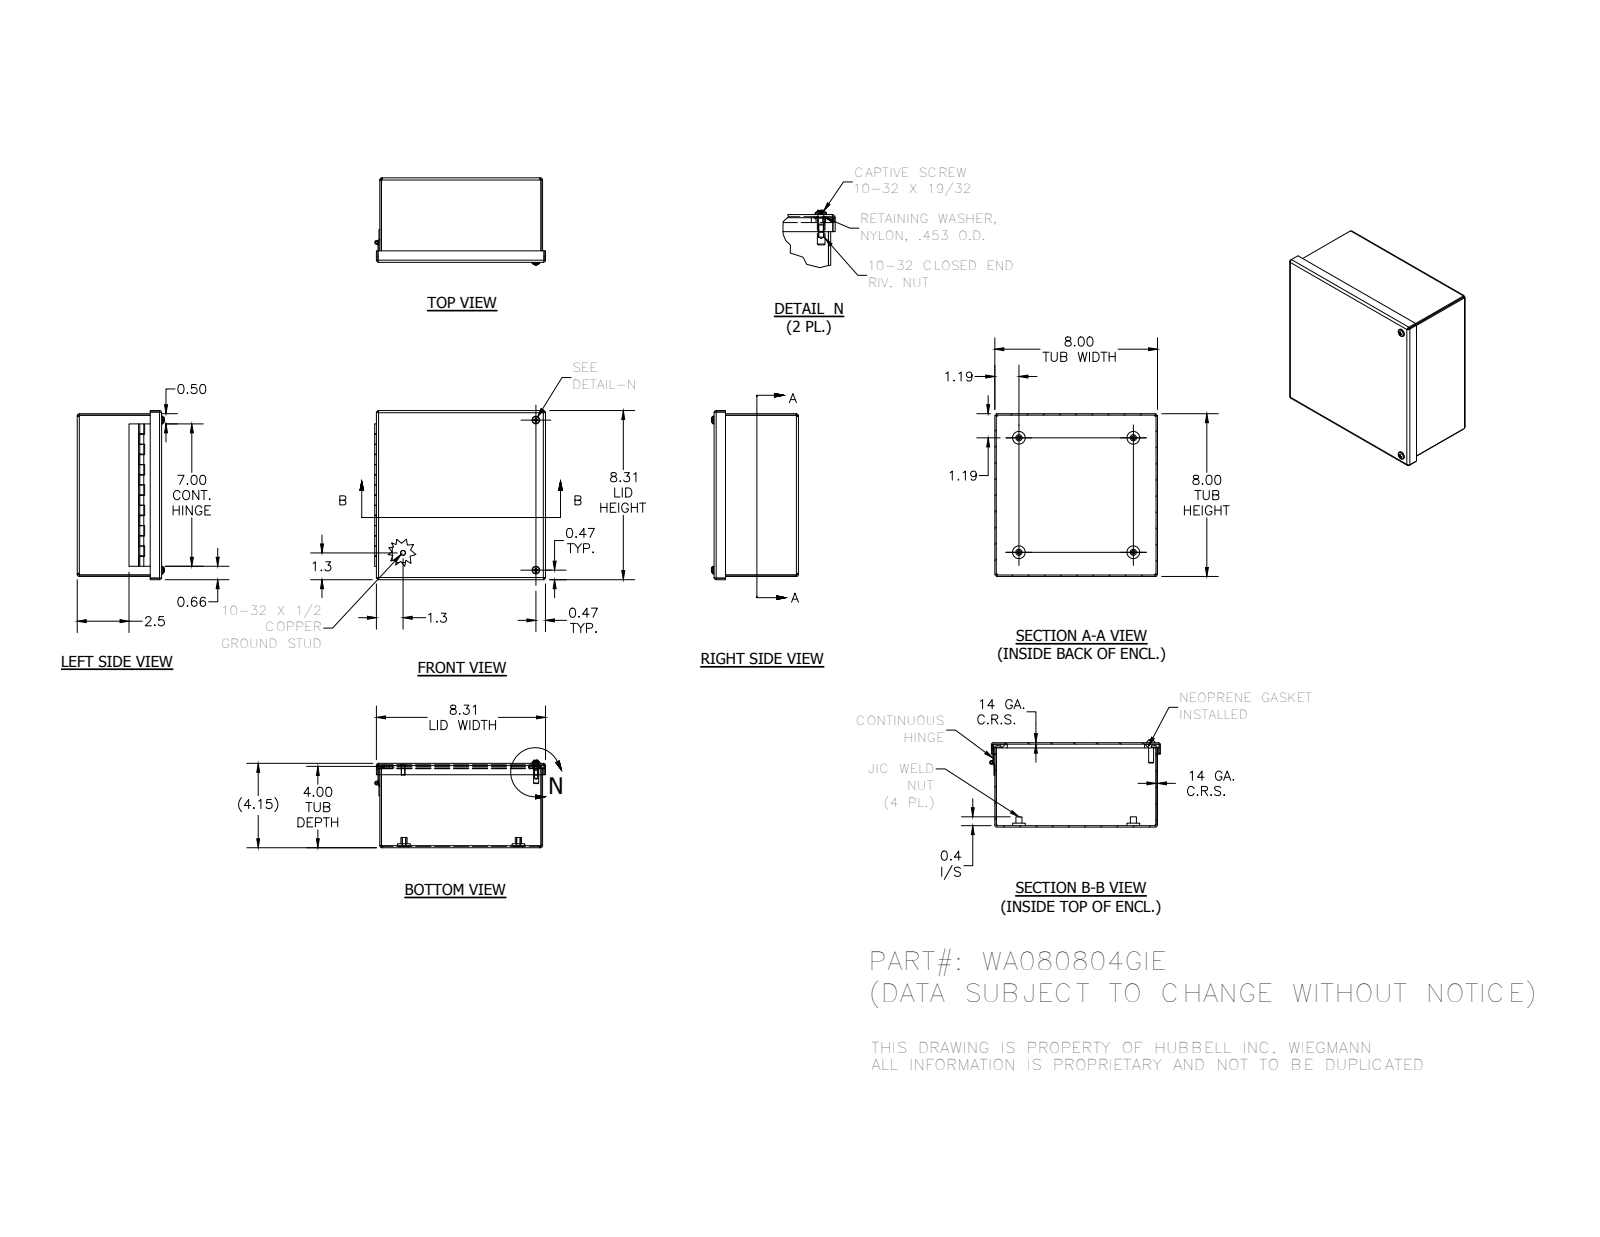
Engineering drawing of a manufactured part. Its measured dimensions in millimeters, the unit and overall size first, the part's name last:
Units: millimetres
Overall size (bounding box): 213.28 × 211.14 × 108.77
Round holes (diameter × count): ⌀3.96 ×6, ⌀6.53 ×4, ⌀7.94 ×4, ⌀4.98 ×2, ⌀7.06 ×2, ⌀7.14 ×2, ⌀2.96 ×1
Round bosses / shafts (diameter × count): ⌀15.88 ×4, ⌀7.62 ×4, ⌀4.83 ×3, ⌀11.51 ×2, ⌀10.31 ×2, ⌀9.47 ×2, ⌀6.3 ×2, ⌀6.35 ×1
Partial cylindrical surfaces — rounded edges, fillets, slot ends (radius × count): R0.79 ×12, R2.67 ×12, R1.78 ×8, R2.27 ×2
Main face-to-face distances: 1.88, 103.58, 201.32, 101.7, 105.46, 203.2, 199.44, 4.76, 6.64, 98.82
Hole centre spacings: 187.32, 166.59, 31.42, 142.88, 187.31, 187.61, 233.49, 264.91
Volume: 418 671 mm³ · Surface area: 424 101 mm²
Bodies: 18 solids, 445 faces (257 planar, 113 cylindrical, 75 other)
Part name (STEP PRODUCT): WA080804GIEBKP; 3499; 328121LH; 328121P (+8 more)
STEP written by: Autodesk Inventor 2014 (AUTOMOTIVE_DESIGN)
